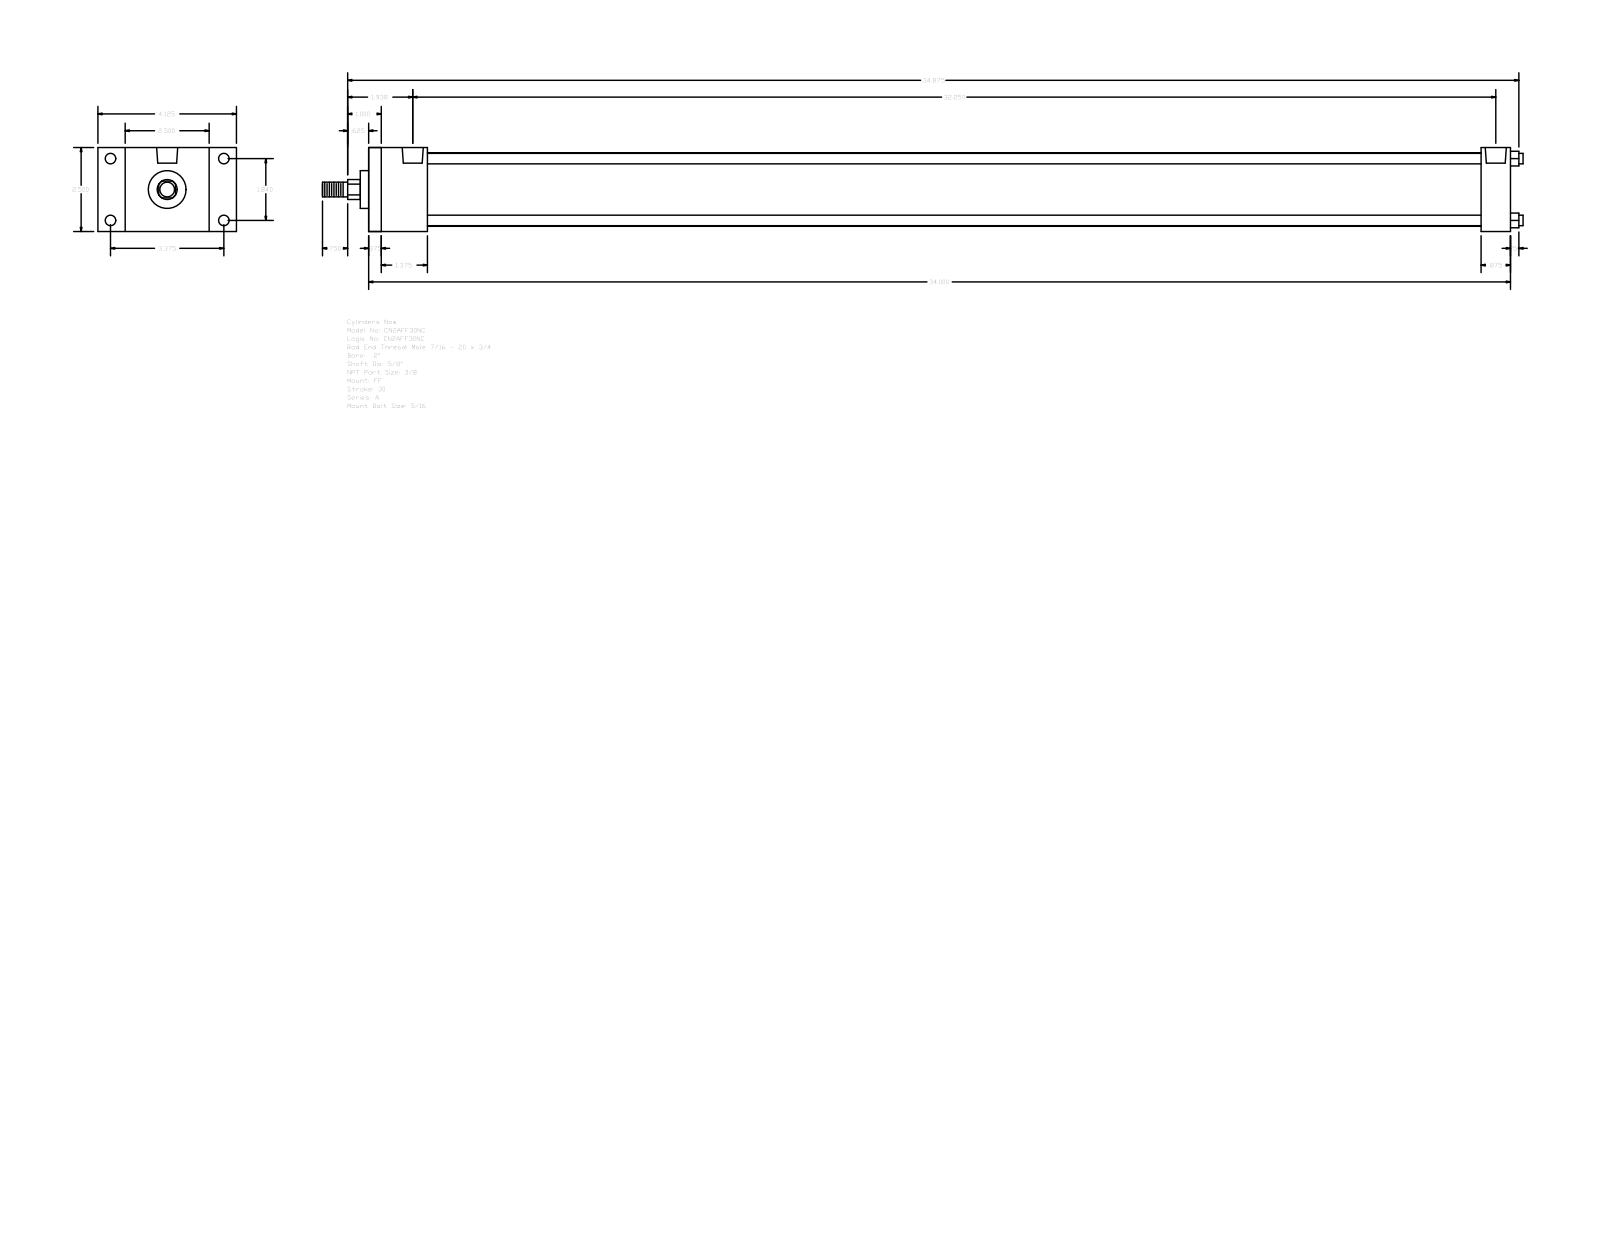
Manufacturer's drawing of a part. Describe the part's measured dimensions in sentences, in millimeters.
The part is named "A_FF__0200_0.625". Its 3-D file was written by "GSSL Pune (CONFIG_CONTROL_DESIGN)". It is 0 solids with 92 faces: 64 planar, 28 cylindrical and 0 other. Overall it measures 908.05 by 104.78 by 63.5 millimeters. Round holes: 4 of diameter 5.56, 4 of diameter 7.94, 2 of diameter 15.93. Round bosses or shafts: 4 of diameter 7.94, 1 of diameter 55.63, 1 of diameter 28.57, 1 of diameter 15.88, 1 of diameter 11.11. Partial cylindrical surfaces (rounded edges, fillets, slot ends): 1 of radius 7.54. The main face-to-face distances are 63.5, 863.6, 9.52, 854.08, 34.93, 44.45, 841.37, 831.85, 796.92, 819.15. The hole center spacings are 46.74, 85.72, 97.63, 811.2, 3.97, 3.98, 815.17, 815.18.
